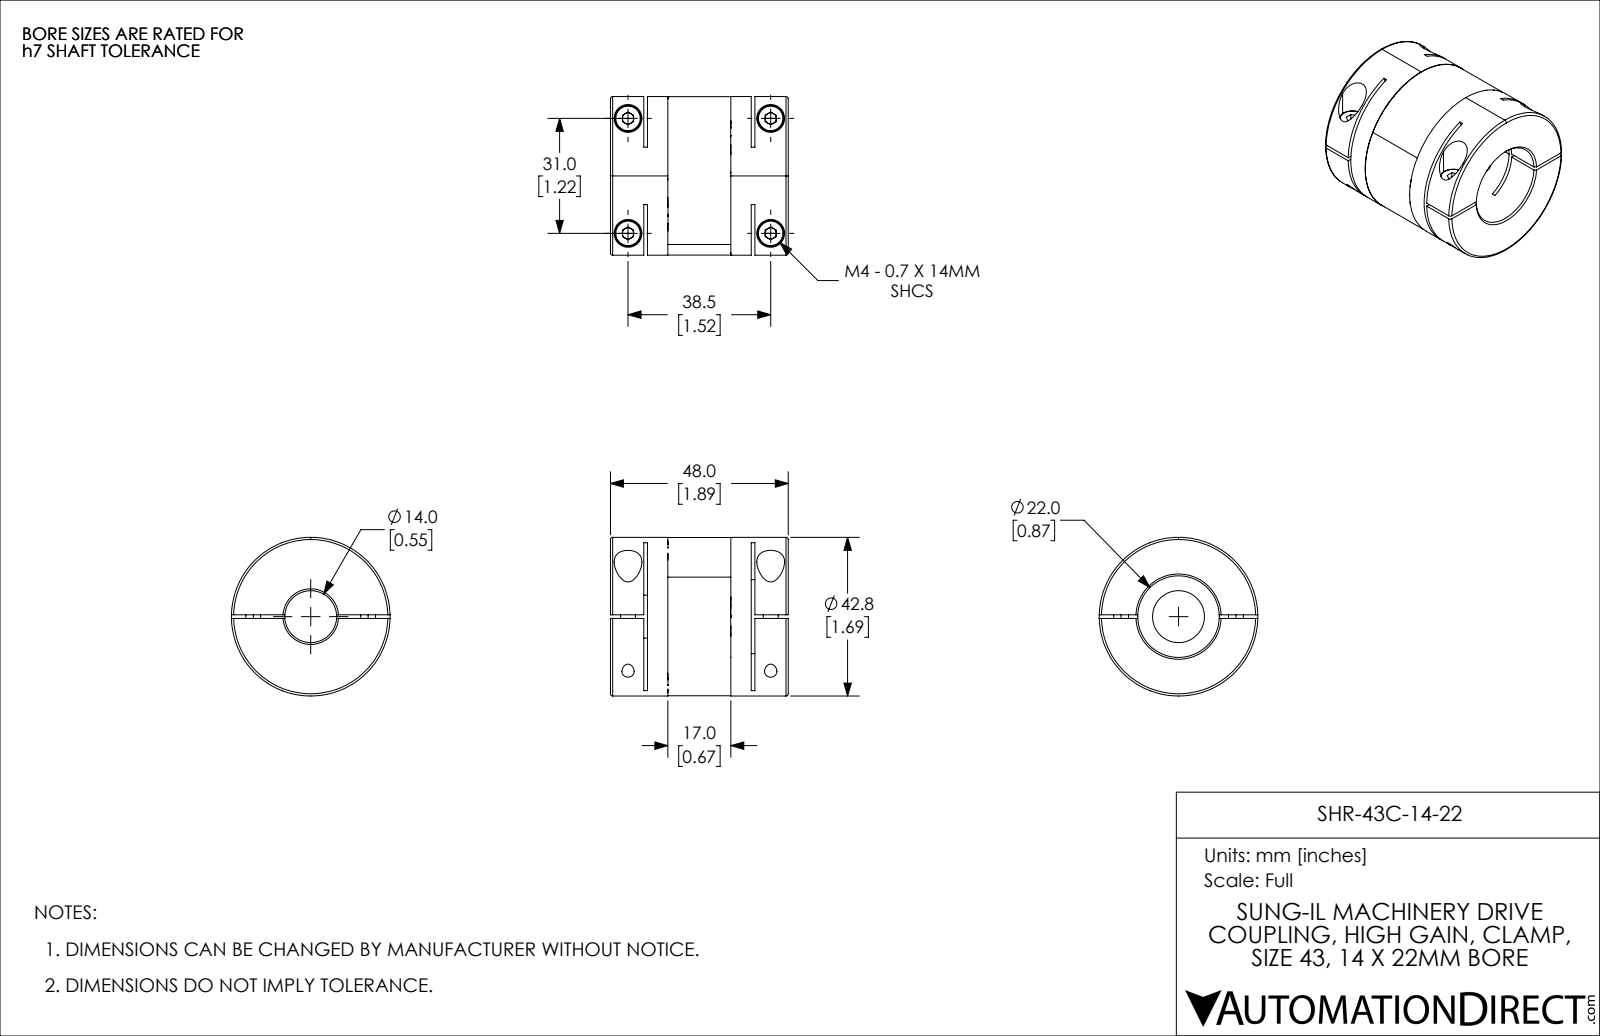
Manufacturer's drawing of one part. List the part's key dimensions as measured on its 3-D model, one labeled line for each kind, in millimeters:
Part name (STEP PRODUCT): SHR-43C-14-22
STEP written by: SolidWorks 2021 (CONFIG_CONTROL_DESIGN)
Units: millimetres
Bodies: 7 solids, 474 faces (134 planar, 180 cylindrical, 160 other)
Overall size (bounding box): 48 × 42.8 × 42.8
Volume: 49 998 mm³ · Surface area: 27 589 mm²
Round holes (diameter × count): ⌀3 ×4, ⌀3.3 ×4, ⌀4.5 ×4, ⌀7.5 ×4, ⌀14 ×1, ⌀22 ×1
Round bosses / shafts (diameter × count): ⌀7 ×4, ⌀4 ×4, ⌀42.8 ×1, ⌀42.7 ×1
Partial cylindrical surfaces — rounded edges, fillets, slot ends (radius × count): R3 ×12, R4 ×12, R11.6 ×6, R50 ×2, R17.5 ×1, R19.5 ×1
Main face-to-face distances: 1, 15.5, 32.5, 9, 10, 5.5, 22.5, 38, 6.5, 23.5
Hole centre spacings: 31, 38.5, 49.43
